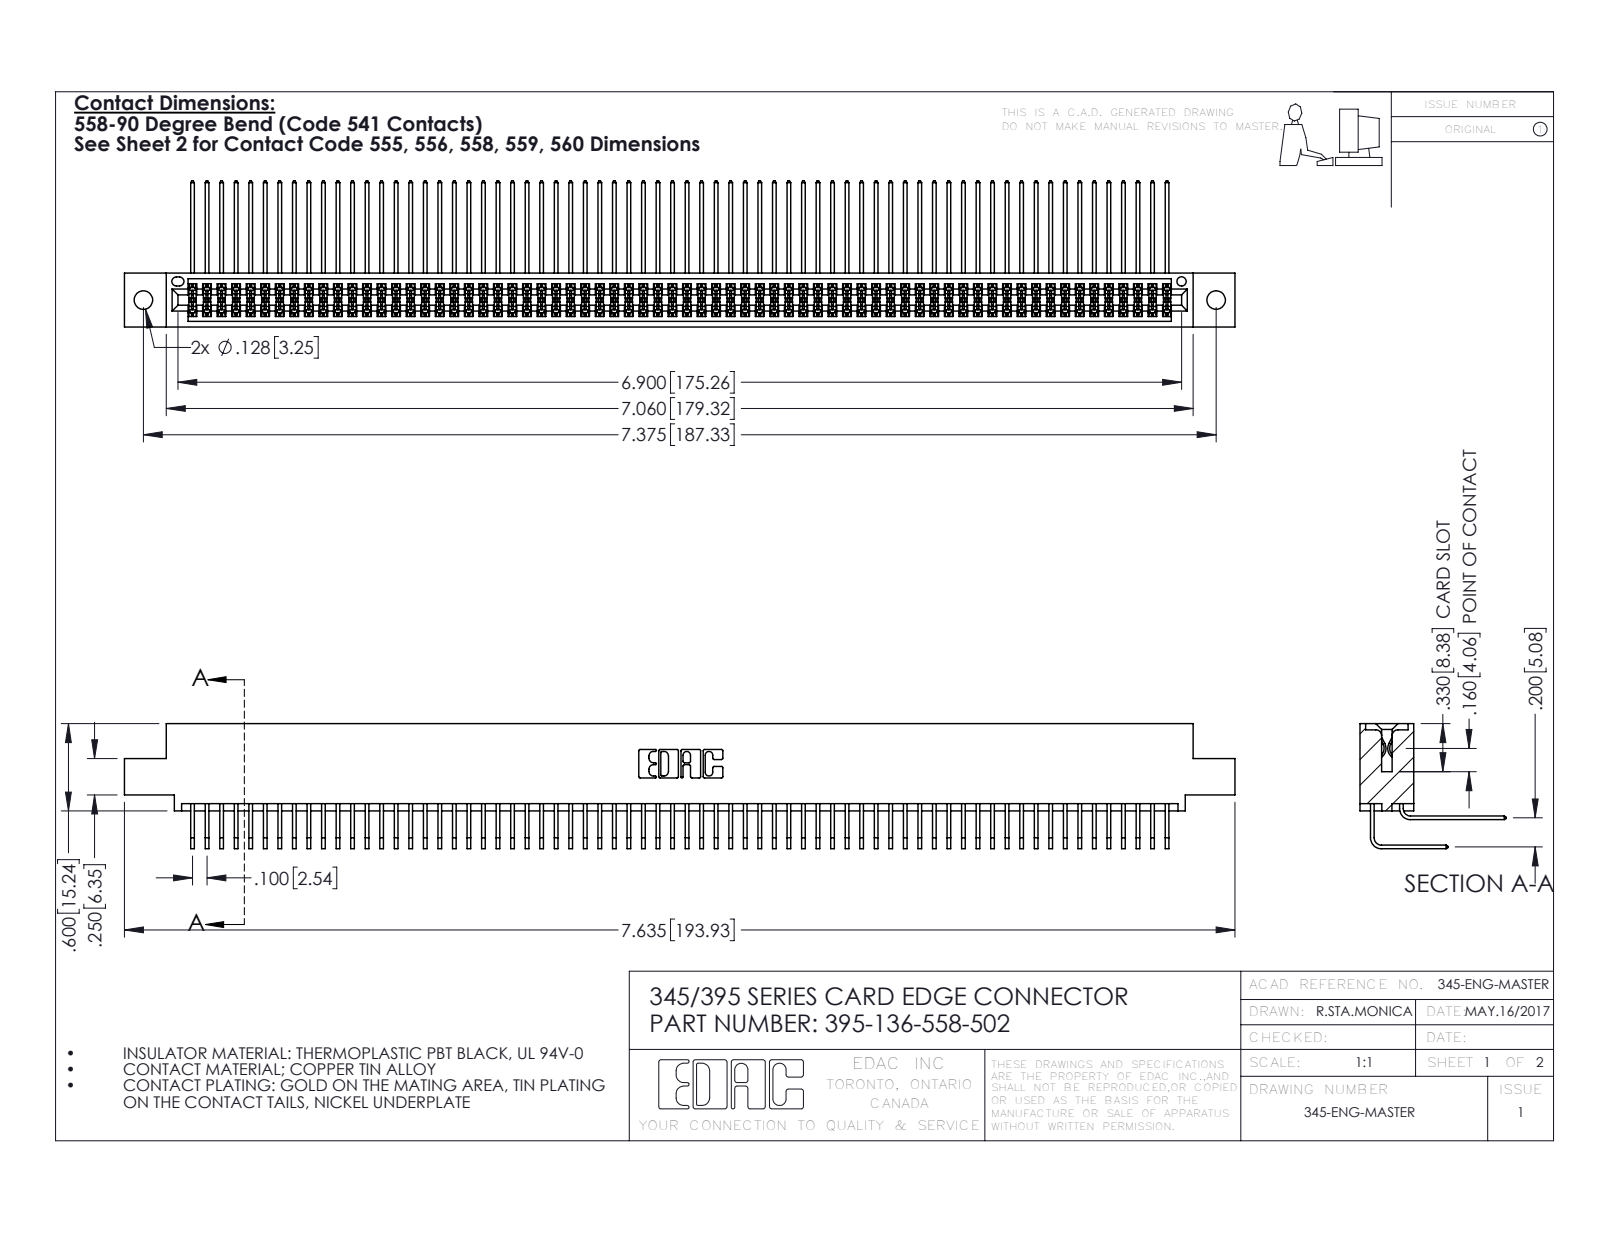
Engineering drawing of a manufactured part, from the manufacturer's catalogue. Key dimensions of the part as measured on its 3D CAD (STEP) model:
Part name (STEP PRODUCT): 345-292-001_558 Tail - 2; 395-136-558-502; 345 Part_0.110 Offset - 0.128 Dia; 345-292-001_558 559 Tail - 1
STEP written by: SolidWorks 2016 (CONFIG_CONTROL_DESIGN)
Units: inches
Bodies: 137 solids, 7202 faces (4844 planar, 2358 cylindrical, 0 other)
Overall size (bounding box): 7.635 × 1.005 × 0.859
Volume: 1.205 in³ · Surface area: 51.48 in²
Round holes (diameter × count): ⌀0.128 ×2, ⌀0.064 ×1
Partial cylindrical surfaces — rounded edges, fillets, slot ends (radius × count): R0.006 ×271, R0.01 ×22, R0.007 ×6, R0.031 ×6, R0.026 ×3, R0.014 ×2, R0.019 ×2, R0.022 ×2
Main face-to-face distances: 0.072, 0.298, 0.2, 0.37, 0.098, 0.272, 0.025, 0.225, 0.025, 0.175
Hole centre spacings: 0.27, 7.139, 7.375
